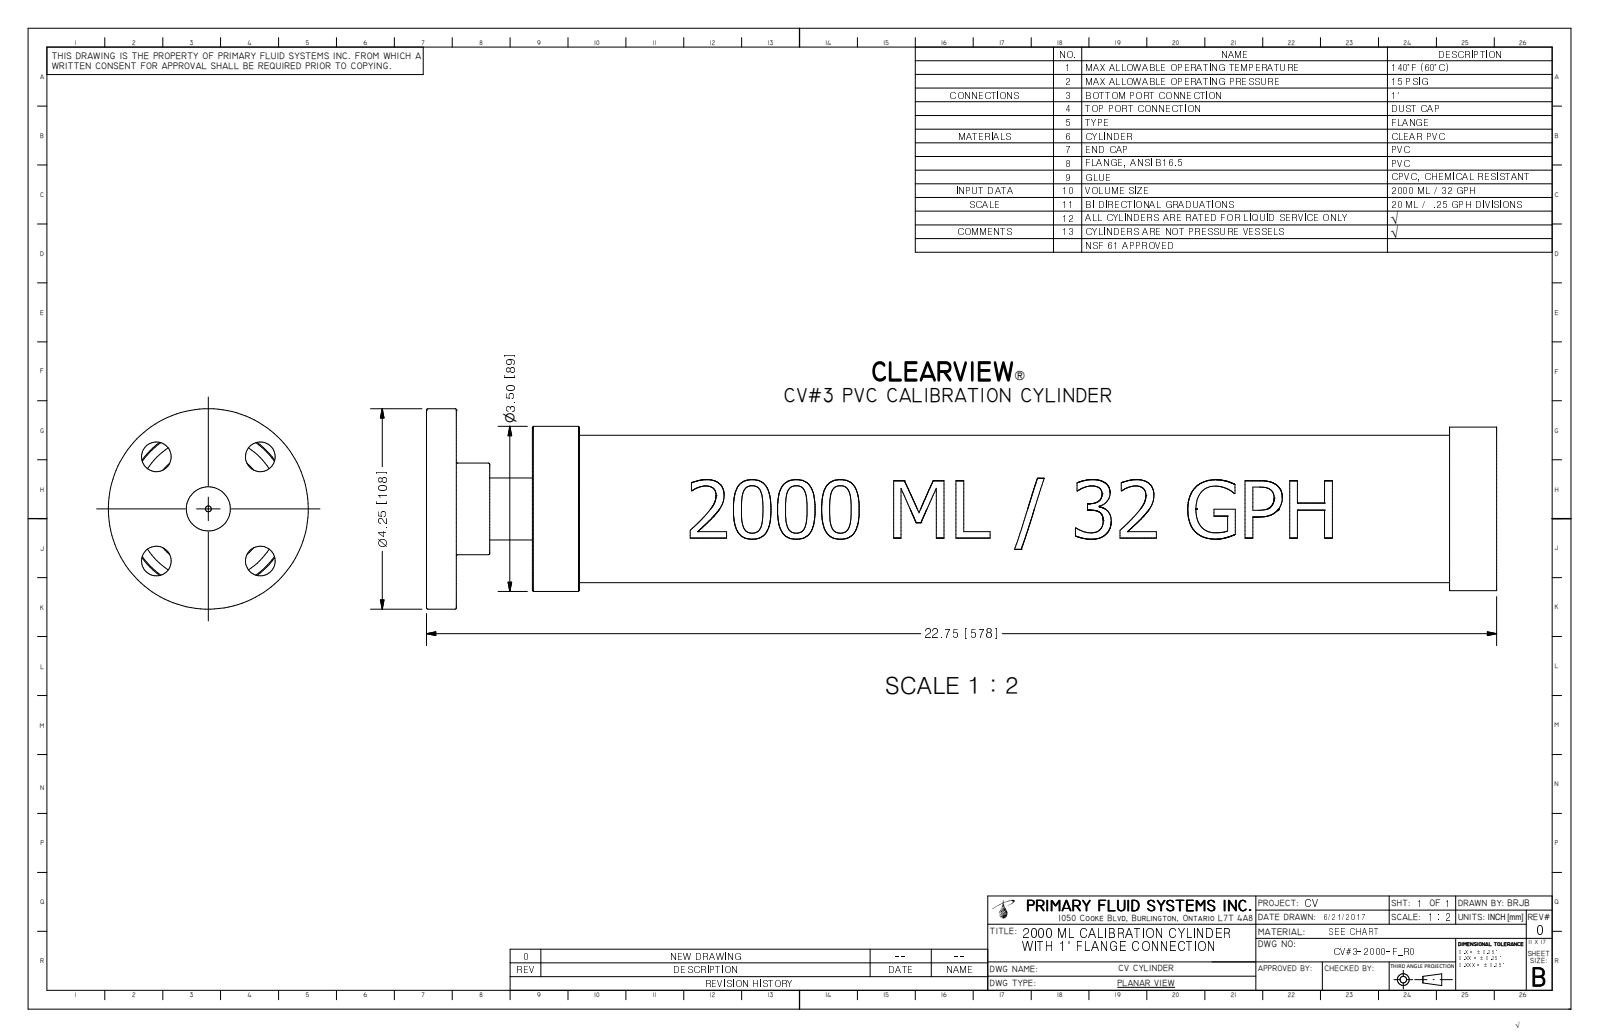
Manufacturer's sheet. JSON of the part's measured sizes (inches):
{"part_name": "PV#3-2000-F_R0", "step_written_by": "Autodesk Inventor 2009 (AUTOMOTIVE_DESIGN)", "units": "inches", "bodies": {"solids": 1, "faces": 281, "planar": 88, "cylindrical": 32, "other": 161}, "overall_size": [22.75, 4.25, 4.25], "volume_in3": 37.14, "surface_area_in2": 516.9, "round_holes": [[0.63, 4], [0.936, 1], [0.957, 1], [1.156, 1], [3.005, 1], [3.156, 1]], "round_bosses_or_shafts": [[4.25, 1], [3.5, 1], [3.467, 1], [3.125, 1], [2.996, 1], [1.941, 1], [1.315, 1]], "partial_cylinders_radius": [[1.561, 1]], "face_to_face_distances": [1, 22.75, 0.635, 22.115, 21.75, 21.115, 19.5, 2.25, 1.615, 20.5], "hole_center_spacings": [1.562, 2.209, 3.125]}
